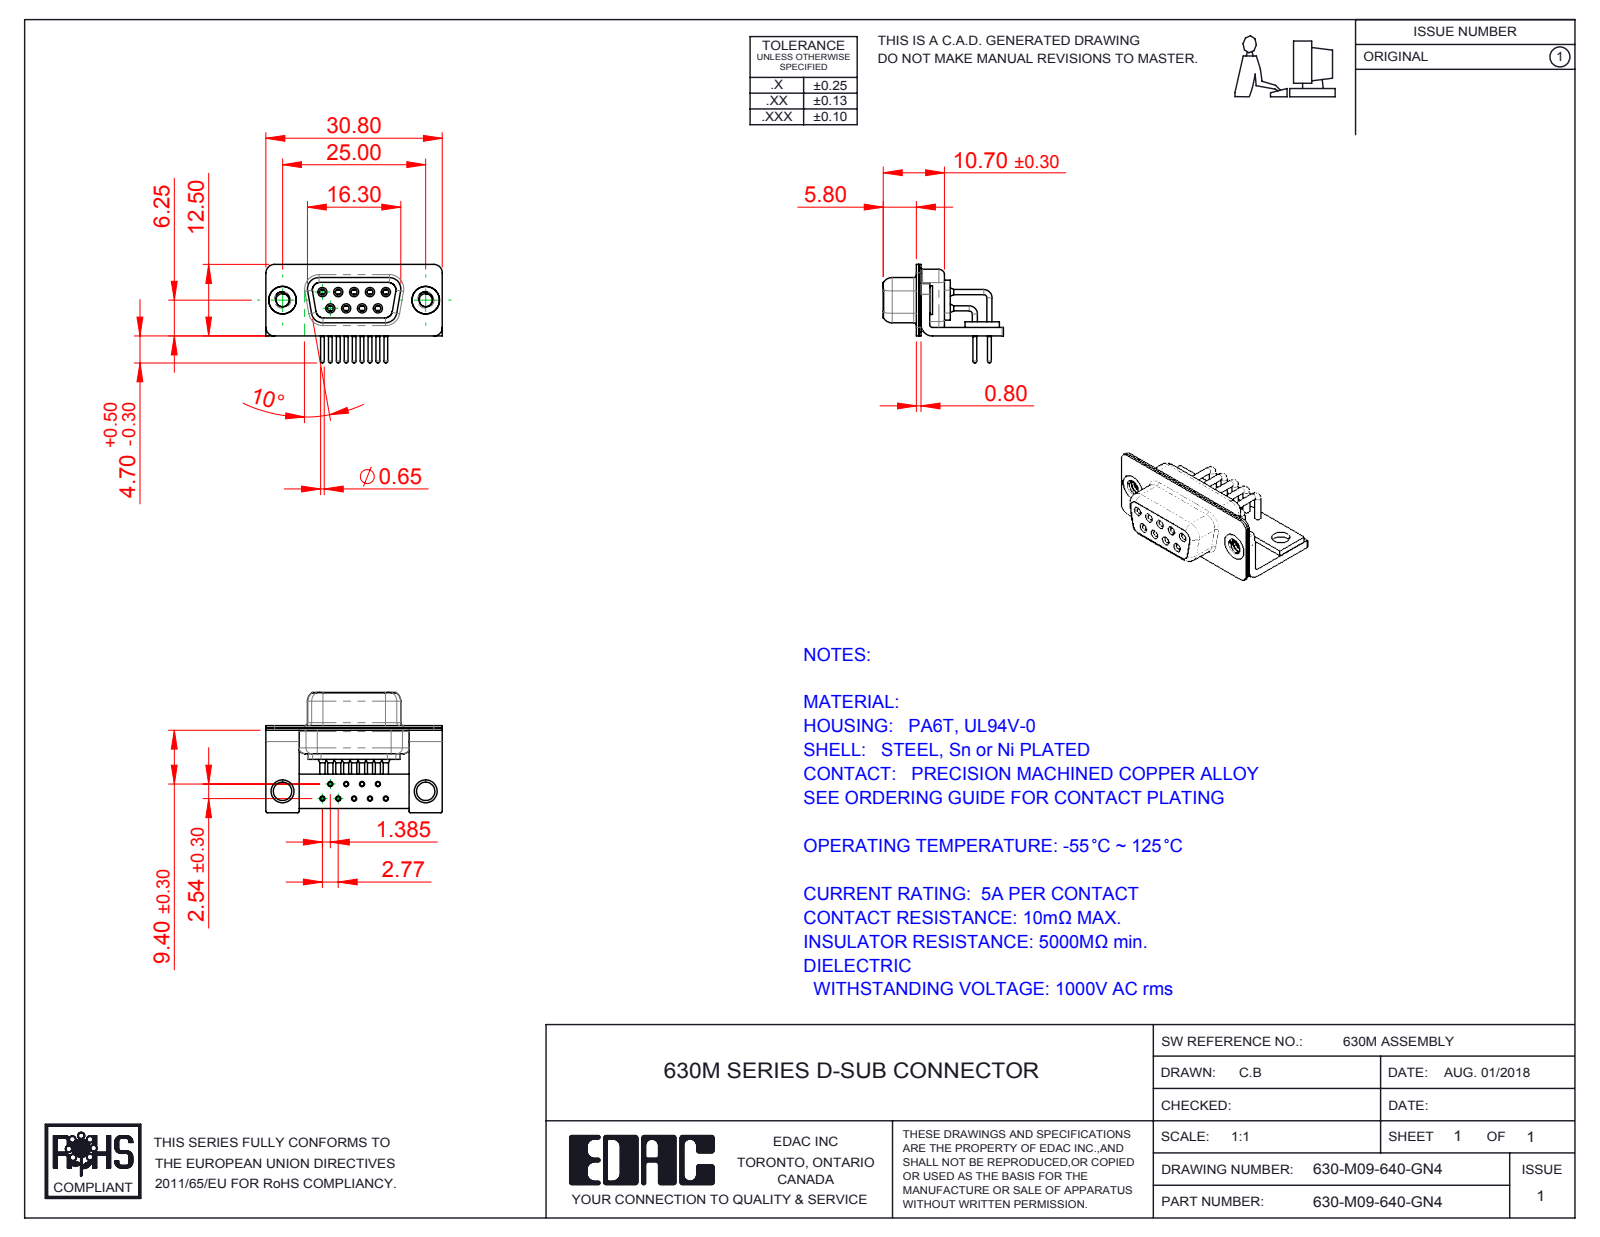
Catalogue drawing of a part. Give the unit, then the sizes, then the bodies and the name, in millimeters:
Units: millimetres
Overall size (bounding box): 30.8 × 21 × 17.2
Round holes (diameter × count): ⌀0.9 ×9, ⌀1 ×9, ⌀1.1 ×9, ⌀1.7 ×9, ⌀1.8 ×9, ⌀2 ×9, ⌀2.26 ×2, ⌀3.2 ×2, ⌀4 ×2, ⌀4.8 ×2
Round bosses / shafts (diameter × count): ⌀1.6 ×9, ⌀1.5 ×9, ⌀0.9 ×9, ⌀0.65 ×9, ⌀5 ×2, ⌀4.9 ×2
Partial cylindrical surfaces — rounded edges, fillets, slot ends (radius × count): R0.25 ×16, R1.5 ×16, R2 ×13, R1.35 ×8, R1.6 ×8, R0.5 ×5, R0.6 ×4, R0.65 ×4
Main face-to-face distances: 0.4, 0.8, 1.5, 2.3, 1.9, 1, 9.35, 1.45, 2.5, 8.95
Hole centre spacings: 2.77, 5.54, 3.16, 4.87, 8.31, 2.89, 2.9, 5.03
Volume: 2 191 mm³ · Surface area: 5 674 mm²
Bodies: 17 solids, 824 faces (228 planar, 384 cylindrical, 212 other)
Part name (STEP PRODUCT): 630M Shell Front_09 Contacts; 630M Shell Rear_09 Contacts; 630M 4-40 Threaded Rivet_Stabilizer; 630-M09-640-GN4 (+5 more)
STEP written by: SolidWorks 2016 (CONFIG_CONTROL_DESIGN)
